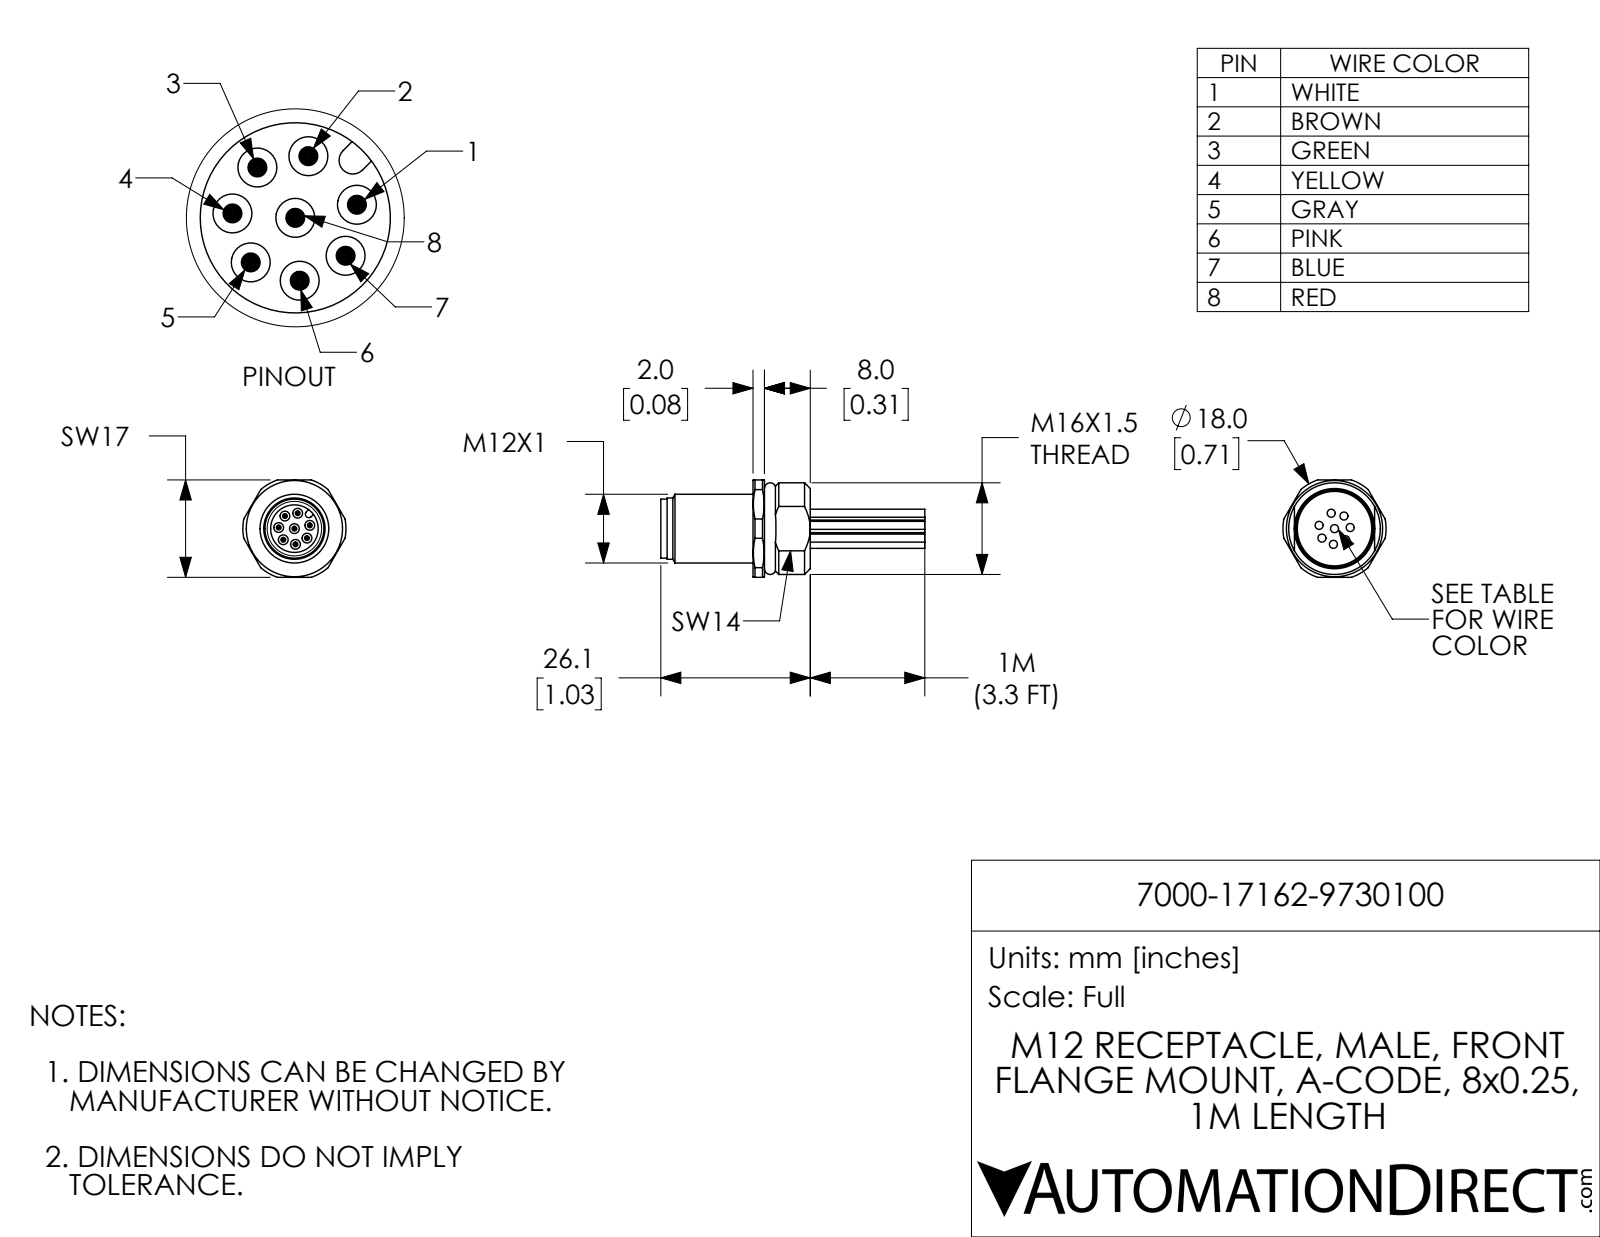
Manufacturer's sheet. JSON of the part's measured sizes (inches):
{"part_name": "7000-17162-9730100", "step_written_by": "SolidWorks 2017 (AUTOMOTIVE_DESIGN)", "units": "inches", "bodies": {"solids": 1, "faces": 142, "planar": 42, "cylindrical": 68, "other": 32}, "overall_size": [1.815, 0.709, 0.669], "volume_in3": 0.209, "surface_area_in2": 4.364, "round_holes": [[0.067, 8], [0.327, 1], [0.512, 1]], "round_bosses_or_shafts": [[0.055, 8], [0.032, 8], [0.472, 1], [0.421, 1], [0.406, 1]], "partial_cylinders_radius": [[0.024, 1], [0.315, 1], [0.354, 1]], "face_to_face_distances": [0.354, 0.276, 0.079, 0.551, 0.669, 0.638, 0.362, 0.283, 0.35, 0.988], "hole_center_spacings": [0.108, 0.163, 0.207, 0.214, 0.089, 0.09, 0.09, 0.183]}
